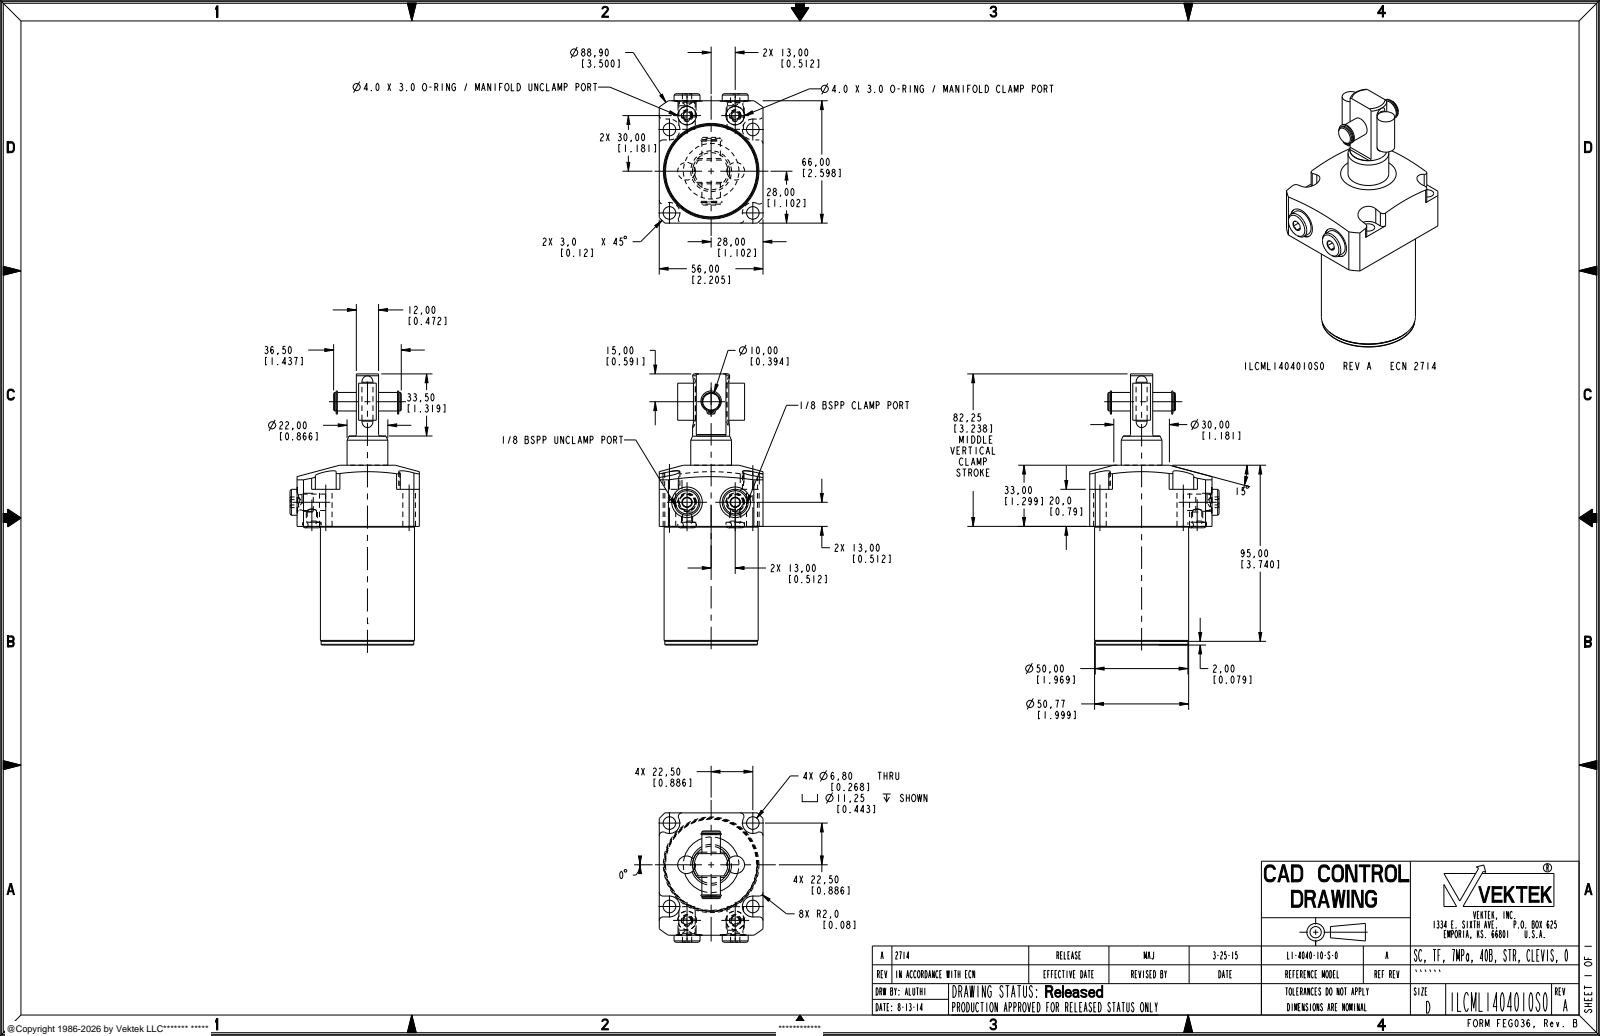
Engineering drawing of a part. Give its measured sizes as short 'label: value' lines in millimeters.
name: ILCML1404010S0
written by: PRO/ENGINEER BY PARAMETRIC TECHNOLOGY CORPORATION, 2013320 (AUTOMOTIVE_DESIGN)
unit: mm
bodies: 5 solids, 245 faces (85 planar, 104 cylindrical, 56 other)
size: 146.25 × 69.81 × 56
volume: 251 419 mm³; area: 34 459 mm²
holes: 4× ⌀5, 4× ⌀6.8, 2× ⌀1.04, 2× ⌀8.84, 2× ⌀10, 2× ⌀16.5
bosses: 2× ⌀14, 2× ⌀9.73, 2× ⌀9.53, 2× ⌀8.25, 2× ⌀6, 1× ⌀50.77, 1× ⌀50, 1× ⌀22
rounds: 8× R2, 4× R5.62, 2× R0.8, 2× R1.04, 2× R1.48, 2× R4.76, 1× R44.45
face distances: 56, 64, 66, 34, 32, 22, 12, 44, 20, 13
hole spacings: 45, 12.1, 26, 36.28, 50.01, 50.61, 53.35, 63.38
